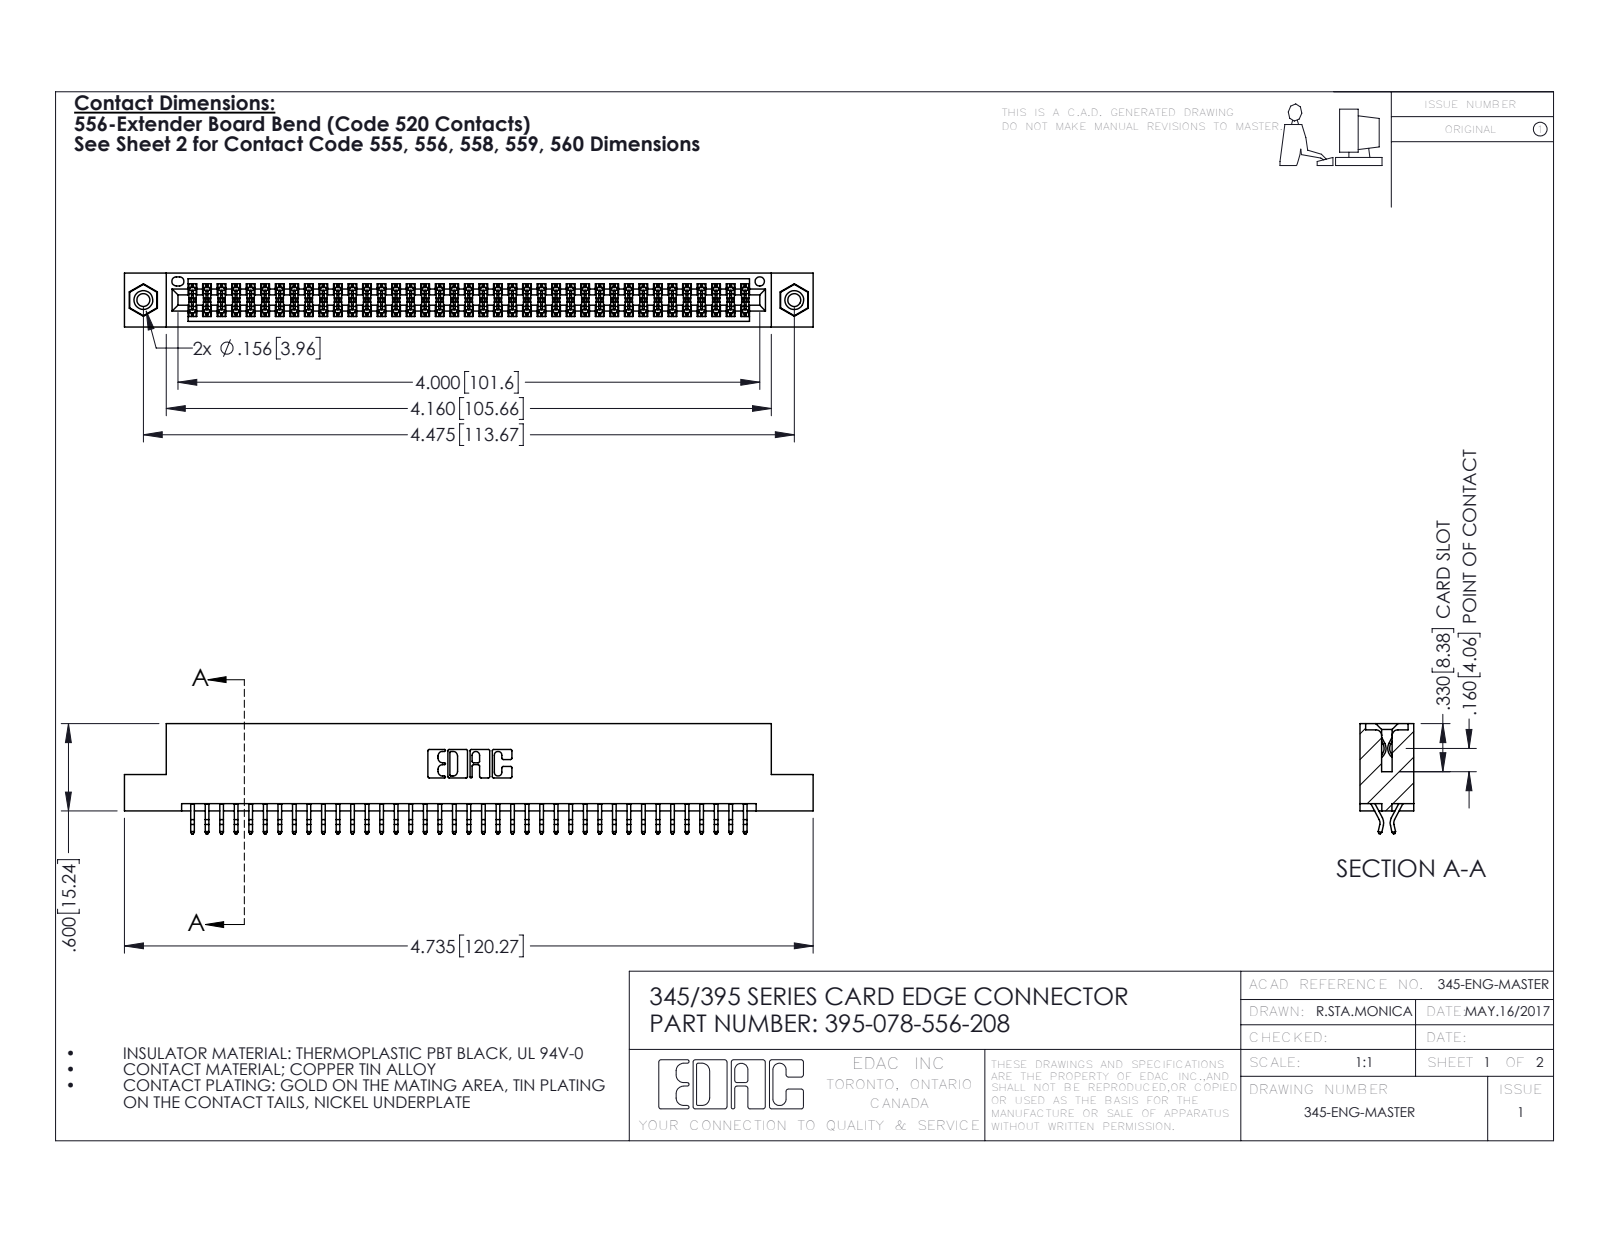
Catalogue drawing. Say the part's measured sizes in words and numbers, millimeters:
The part is named "395-078-556-208; 345-250-001_345-250-003-102; 345-292-001_556 Tail; 345 Part_Flush Mounting Lugs - 0.156 Dia-TI". Its 3-D file was written by "SolidWorks 2016 (CONFIG_CONTROL_DESIGN)". It is 81 solids with 4554 faces: 2998 planar, 1540 cylindrical and 16 other. Overall it measures 120.3 by 19.2 by 9.4 millimeters. Its volume is 11 700 cubic millimeters and its surface area 17 100 square millimeters. Round holes: 2 of diameter 2.3, 2 of diameter 3.2, 2 of diameter 4, 1 of diameter 1.6. Round bosses or shafts: 2 of diameter 3.9. Partial cylindrical surfaces (rounded edges, fillets, slot ends): 117 of radius 0.2, 22 of radius 0.3, 6 of radius 0.2, 6 of radius 0.8, 3 of radius 0.7, 2 of radius 0.3, 2 of radius 0.4, 2 of radius 0.5. The main face-to-face distances are 1.8, 7.6, 9.4, 5.1, 0.6, 2.5, 6.9, 5.7, 4.4, 3.8. The hole center spacings are 6.9, 107.7, 113.7.
